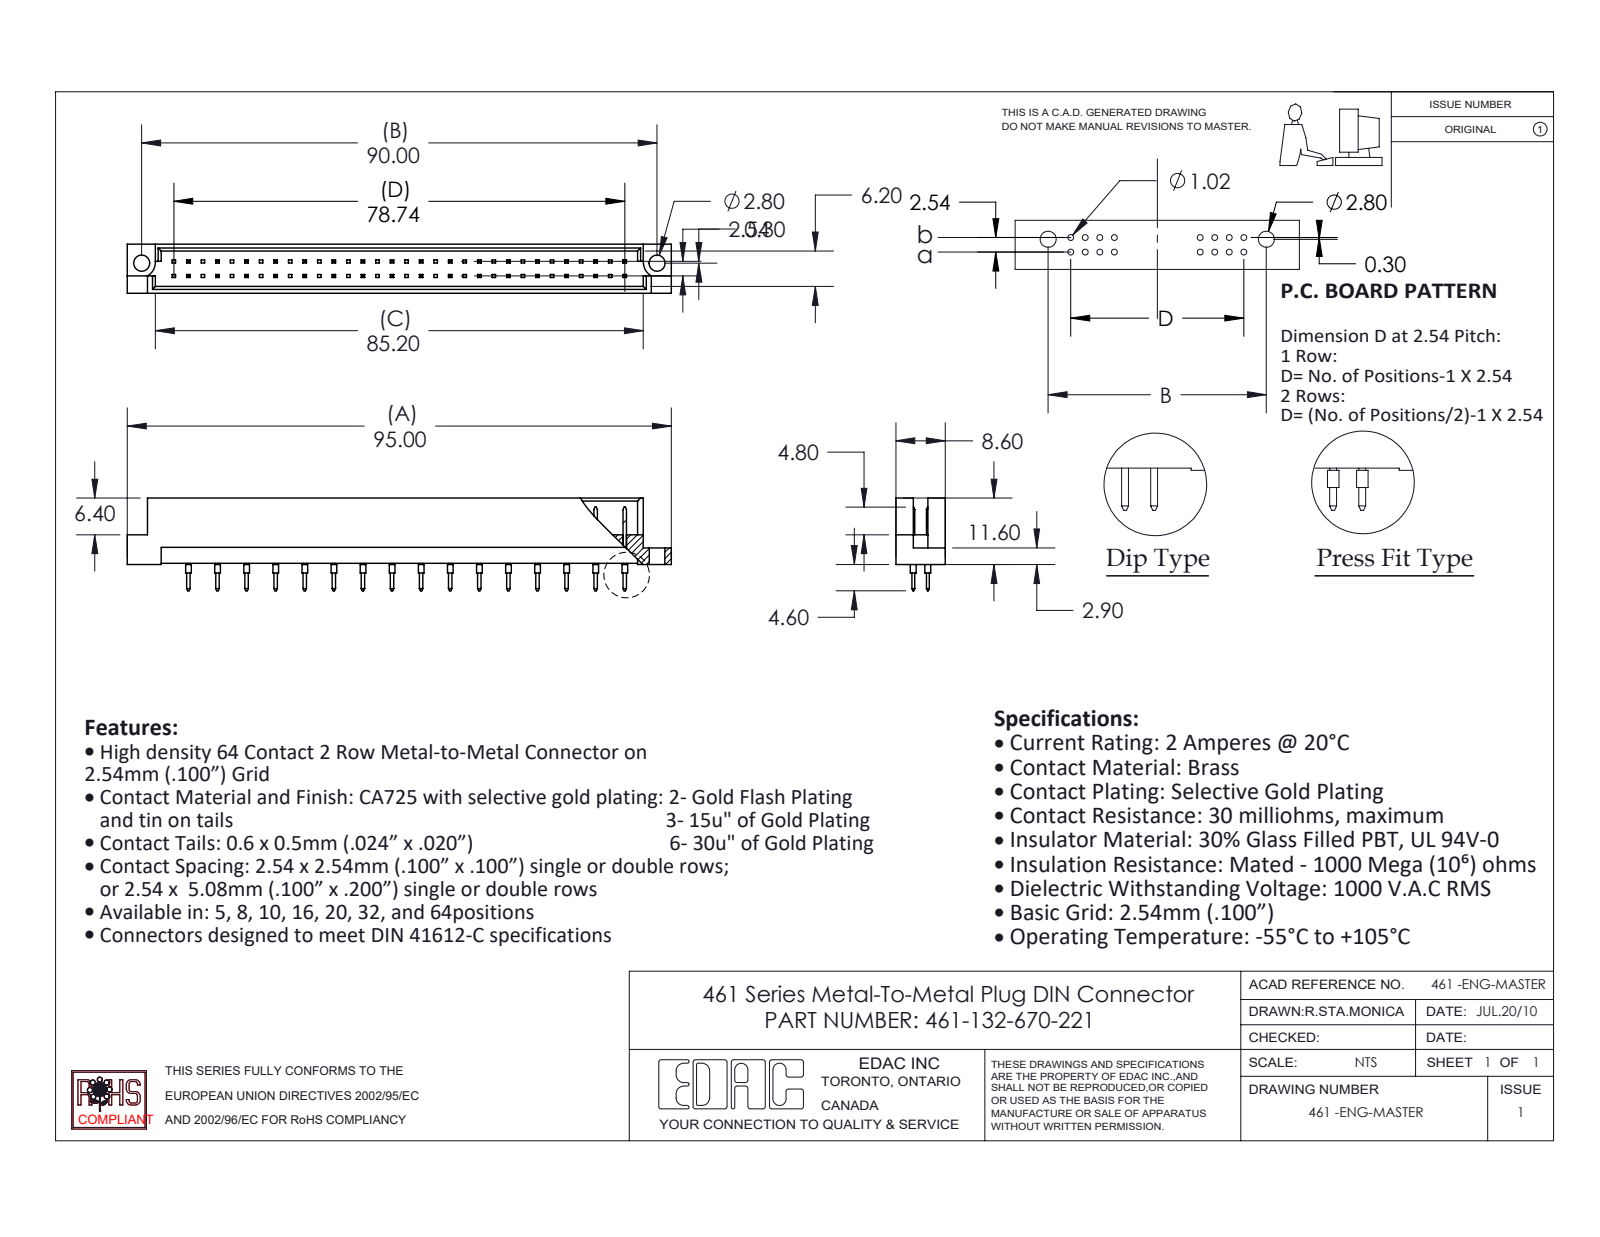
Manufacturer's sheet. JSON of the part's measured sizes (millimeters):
{"part_name": "461 Part_64; 461-290_70; 461-132-670-221", "step_written_by": "SolidWorks 2020 (CONFIG_CONTROL_DESIGN)", "units": "millimeters", "bodies": {"solids": 33, "faces": 1009, "planar": 938, "cylindrical": 71, "other": 0}, "overall_size": [95, 16.2, 8.6], "volume_mm3": 4816, "surface_area_mm2": 6763, "round_holes": [[2.8, 2]], "round_bosses_or_shafts": [[1, 32]], "partial_cylinders_radius": [[2.8, 2]], "face_to_face_distances": [1.2, 7.4, 8.6, 6.2, 5, 2.54, 1.58, 3.28, 5.32, 2.08], "hole_center_spacings": [90]}
